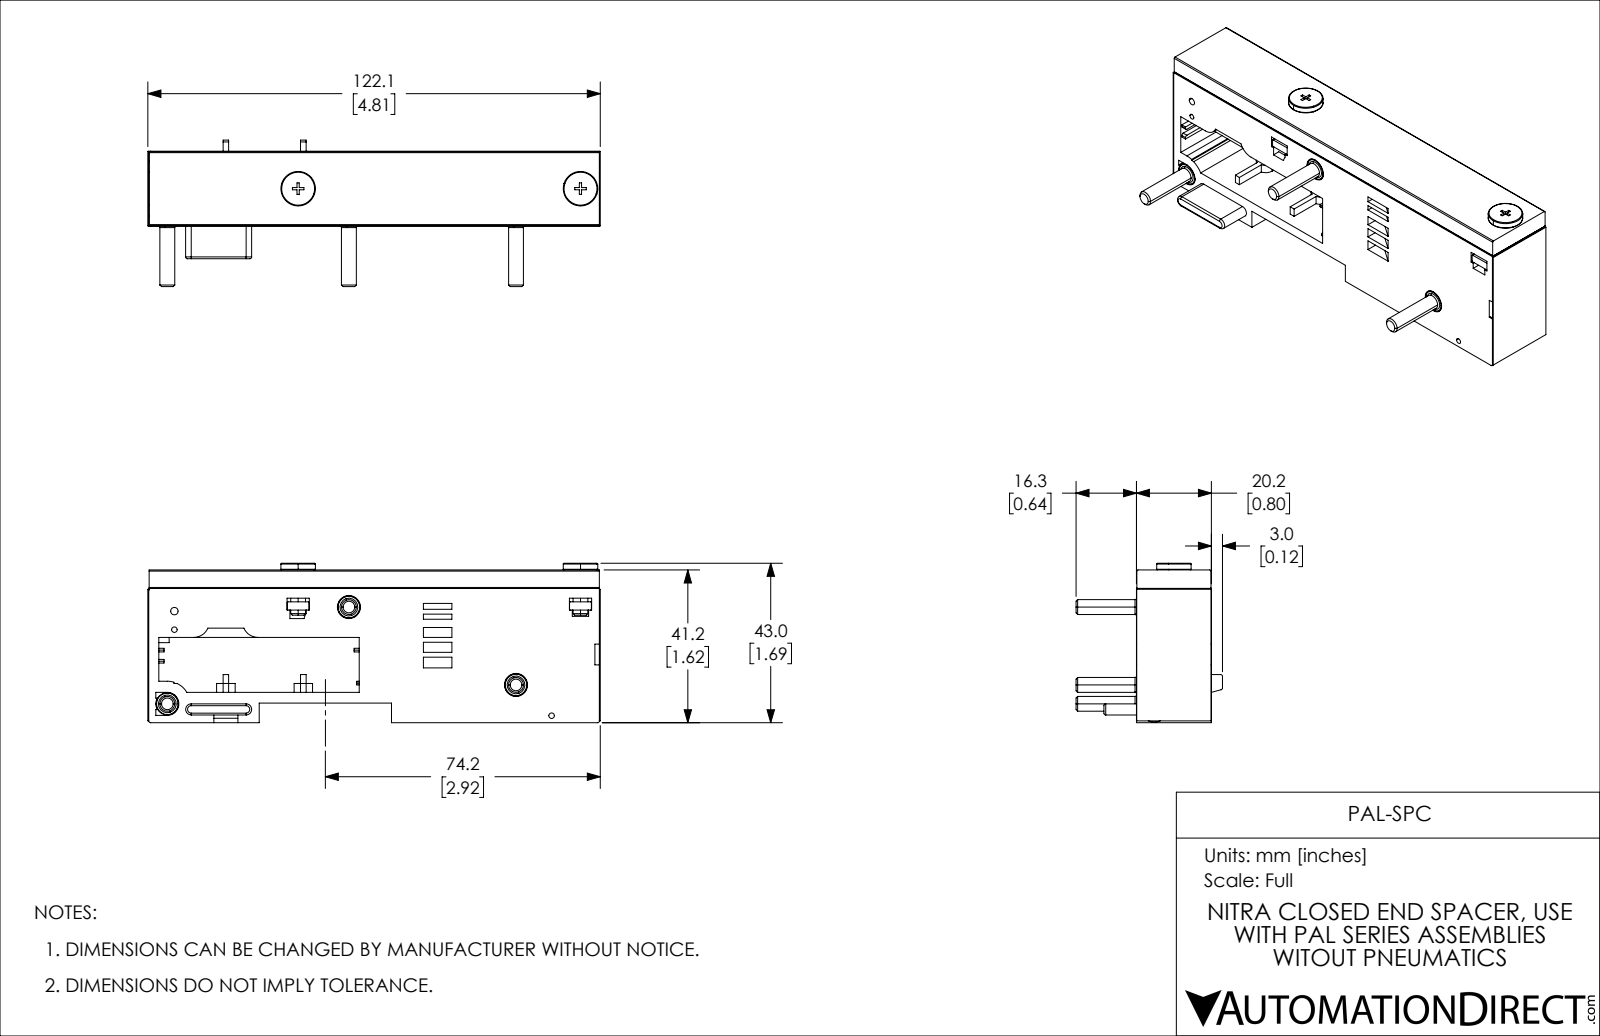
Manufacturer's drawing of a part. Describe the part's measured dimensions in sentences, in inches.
The part is named "PAL-SPC". Its 3-D file was written by "SolidWorks 2019 (CONFIG_CONTROL_DESIGN)". It is 13 solids with 1037 faces: 848 planar, 139 cylindrical and 50 other. Overall it measures 4.807 by 1.693 by 1.555 inches. Its volume is 4.378 cubic inches and its surface area 46.92 square inches. Round holes: 3 of diameter 0.128, 3 of diameter 0.157, 2 of diameter 0.059, 2 of diameter 0.079, 2 of diameter 0.165, 2 of diameter 0.177, 2 of diameter 0.244, 1 of diameter 0.189, 1 of diameter 0.362, 1 of diameter 0.366. Round bosses or shafts: 5 of diameter 0.157, 3 of diameter 0.236, 2 of diameter 0.366, 1 of diameter 0.374. Partial cylindrical surfaces (rounded edges, fillets, slot ends): 10 of radius 0.02, 8 of radius 0.008, 4 of radius 0.012, 3 of radius 0.082, 2 of radius 0.031, 2 of radius 0.039, 2 of radius 0.059, 2 of radius 0.098. The main face-to-face distances are 0.795, 1.622, 0.717, 0.323, 0.791, 0.906, 0.583, 0.209, 1.299, 0.697. The hole center spacings are 0.172, 0.197, 0.22, 0.221, 0.234, 0.356, 0.5, 0.646.
